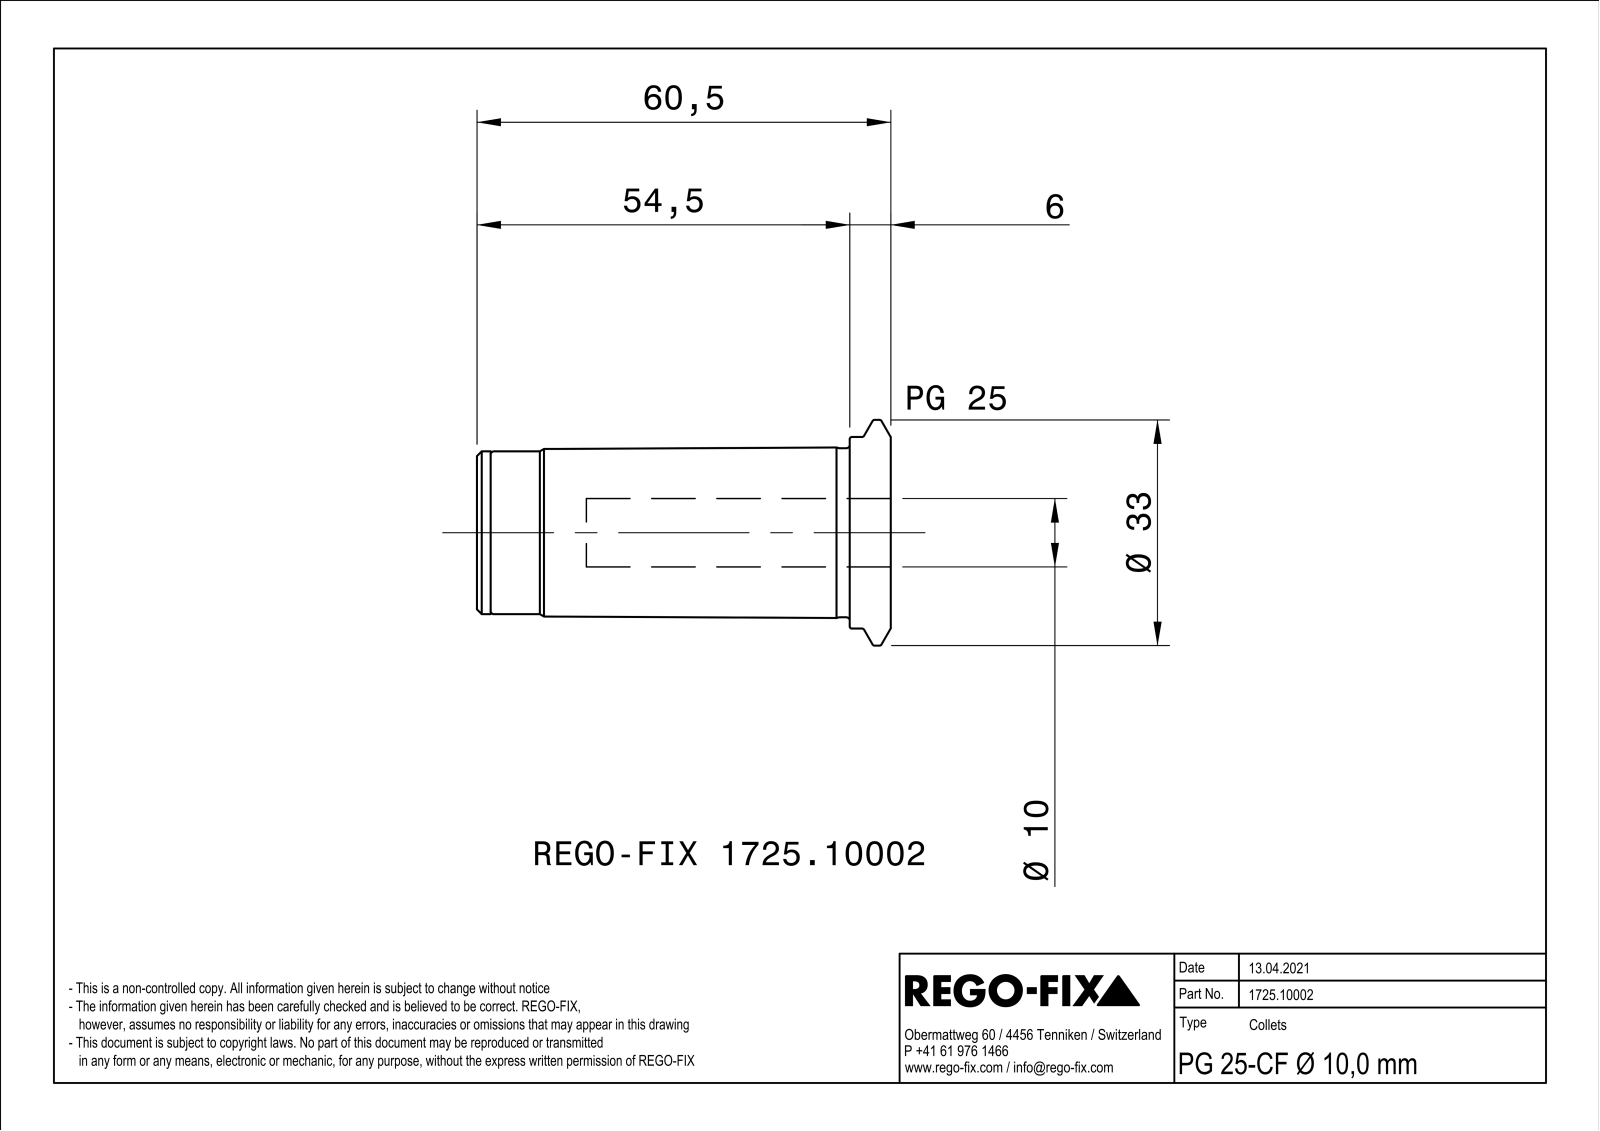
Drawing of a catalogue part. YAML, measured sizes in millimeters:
part_name: "NOCUT"
step_written_by: "SIEMENS PLM Software Solid Edge ST10 (AUTOMOTIVE_DESIGN)"
units: millimeters
bodies: {solids: 1, faces: 89, planar: 23, cylindrical: 27, other: 39}
overall_size: [60.5, 33, 32.99]
volume: 23735
surface_area: 11152
round_holes:
  - {diameter: 2.5, count: 3}
  - {diameter: 5.2, count: 1}
  - {diameter: 6.92, count: 1}
  - {diameter: 8.2, count: 1}
  - {diameter: 10, count: 1}
  - {diameter: 20.92, count: 1}
  - {diameter: 22.2, count: 1}
round_bosses_or_shafts:
  - {diameter: 33, count: 1}
  - {diameter: 28, count: 1}
  - {diameter: 24.7, count: 1}
  - {diameter: 23.8, count: 1}
  - {diameter: 20.4, count: 1}
  - {diameter: 12, count: 1}
partial_cylinders:
  - {radius: 0.75, count: 3}
face_to_face_distances: [1, 60.5, 52.6, 7.9, 58.5, 5.9, 2, 50, 2.6, 8.5]
hole_center_spacings: [7.75, 13.43, 13.42]
